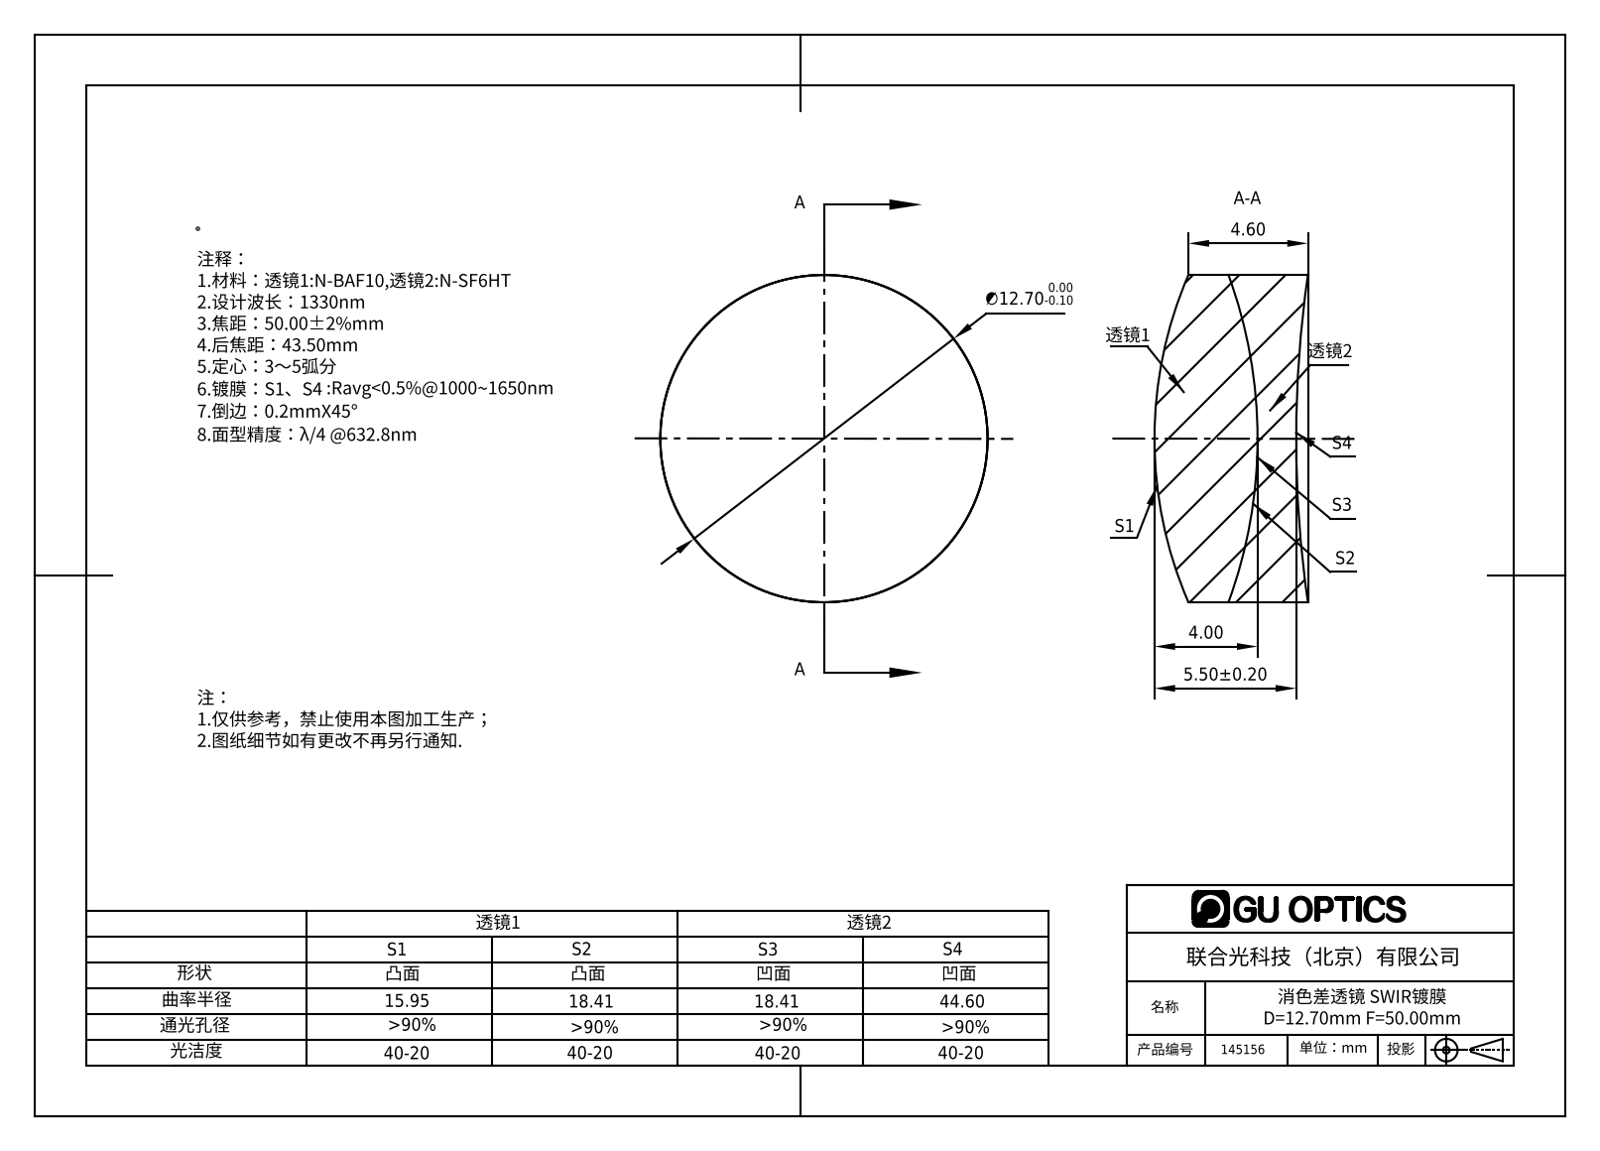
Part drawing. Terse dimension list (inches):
name: 145156
written by: SolidWorks 2016 (AUTOMOTIVE_DESIGN)
unit: in
bodies: 2 solids, 12 faces (0 planar, 4 cylindrical, 8 other)
size: 0.5 × 0.5 × 0.234
volume: 0.039 in³; area: 1.09 in²
bosses: 1× ⌀0.5
